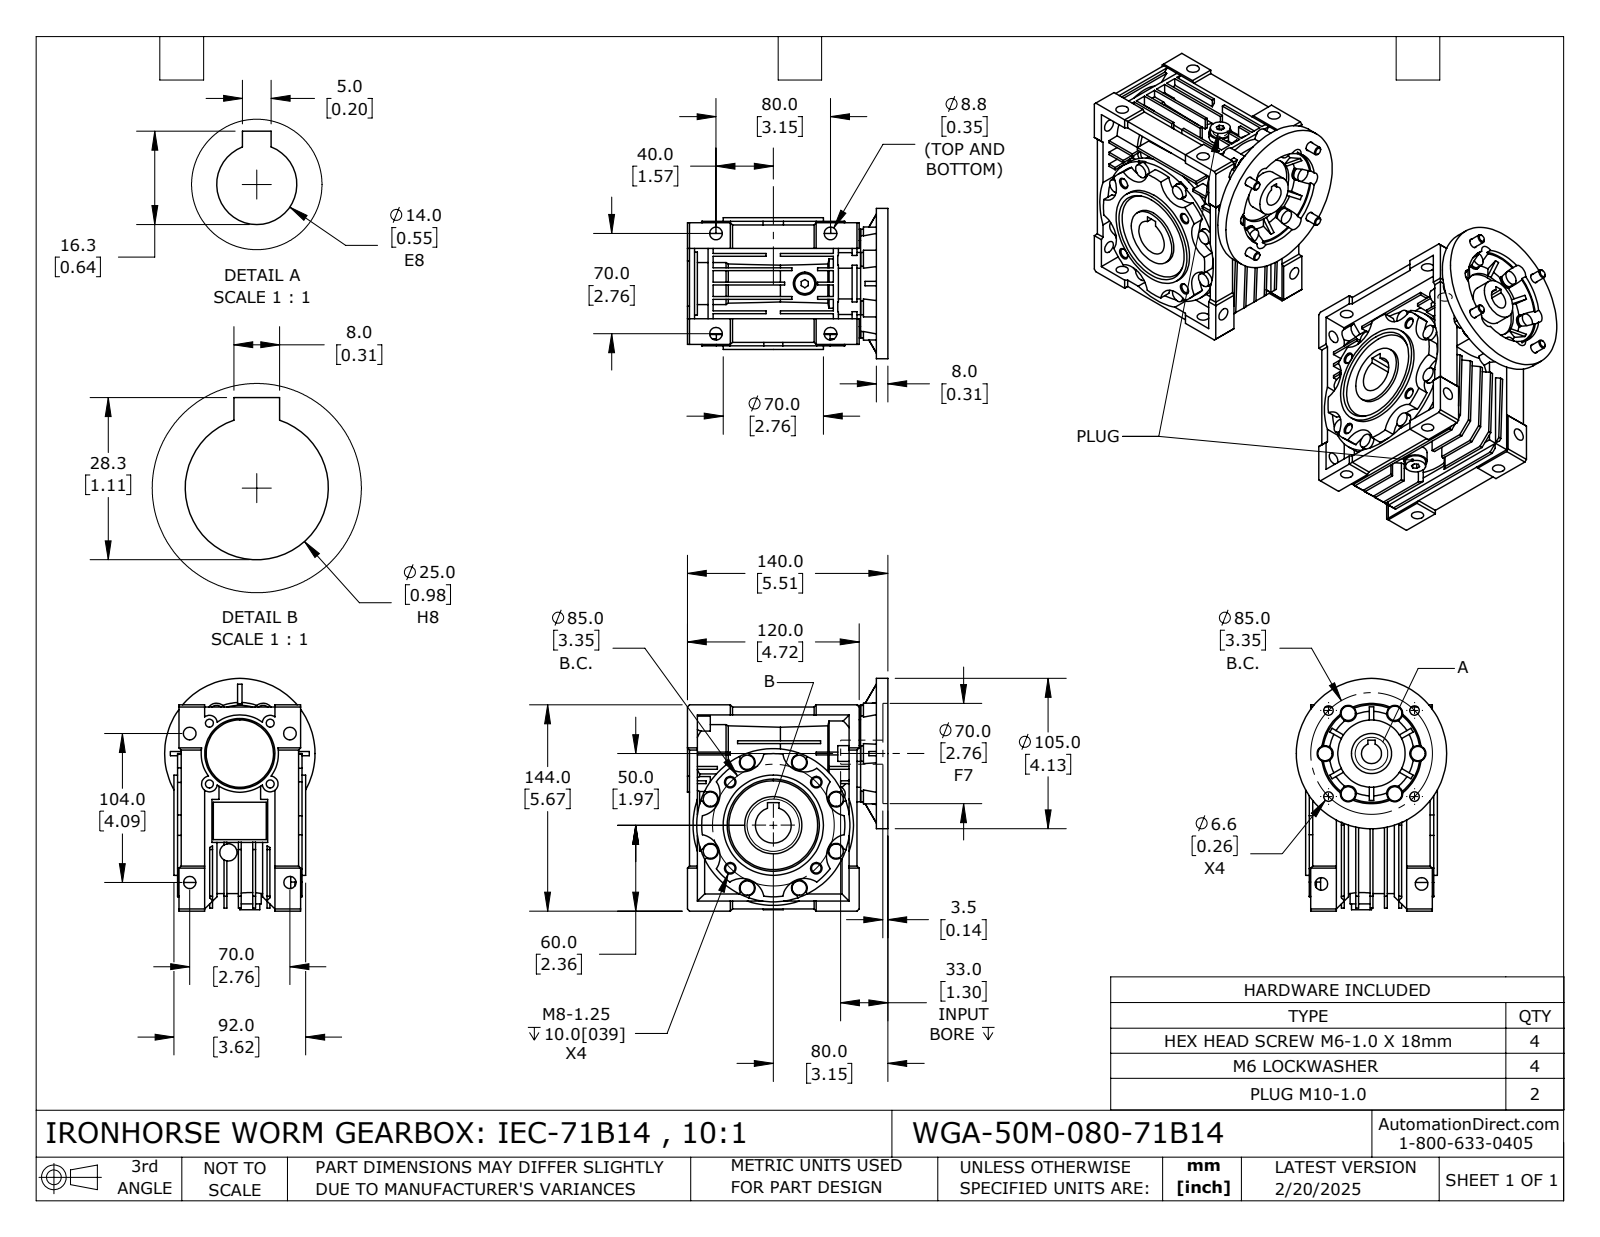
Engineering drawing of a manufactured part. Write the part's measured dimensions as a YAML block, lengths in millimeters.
part_name: "WGA-50M-080-71B14"
step_written_by: "SolidWorks 2024 (CONFIG_CONTROL_DESIGN)"
units: millimeters
bodies: {solids: 15, faces: 1132, planar: 615, cylindrical: 372, other: 145}
overall_size: [162.5, 148.5, 105]
volume: 1065000
surface_area: 235209
round_holes:
  - {diameter: 8.8, count: 8}
  - {diameter: 8.5, count: 6}
  - {diameter: 5.55, count: 4}
  - {diameter: 6.1, count: 4}
  - {diameter: 6.6, count: 4}
  - {diameter: 6.65, count: 2}
  - {diameter: 6.65, count: 2}
  - {diameter: 9, count: 2}
  - {diameter: 14, count: 1}
  - {diameter: 15, count: 1}
  - {diameter: 25, count: 1}
  - {diameter: 28, count: 1}
round_bosses_or_shafts:
  - {diameter: 10, count: 14}
  - {diameter: 12.2, count: 4}
  - {diameter: 6, count: 4}
  - {diameter: 16, count: 2}
  - {diameter: 14, count: 2}
  - {diameter: 9.8, count: 2}
  - {diameter: 8.3, count: 2}
  - {diameter: 107, count: 1}
partial_cylinders:
  - {radius: 5.5, count: 18}
  - {radius: 6, count: 8}
  - {radius: 15, count: 8}
  - {radius: 15.5, count: 8}
  - {radius: 5.75, count: 6}
  - {radius: 7, count: 6}
  - {radius: 20.76, count: 1}
  - {radius: 35, count: 1}
face_to_face_distances: [8, 2, 10, 7, 1.5, 5.5, 20, 12, 55, 35]
hole_center_spacings: [42.5, 52.02, 60.1, 70, 12.5, 30, 42.42, 72.49]
